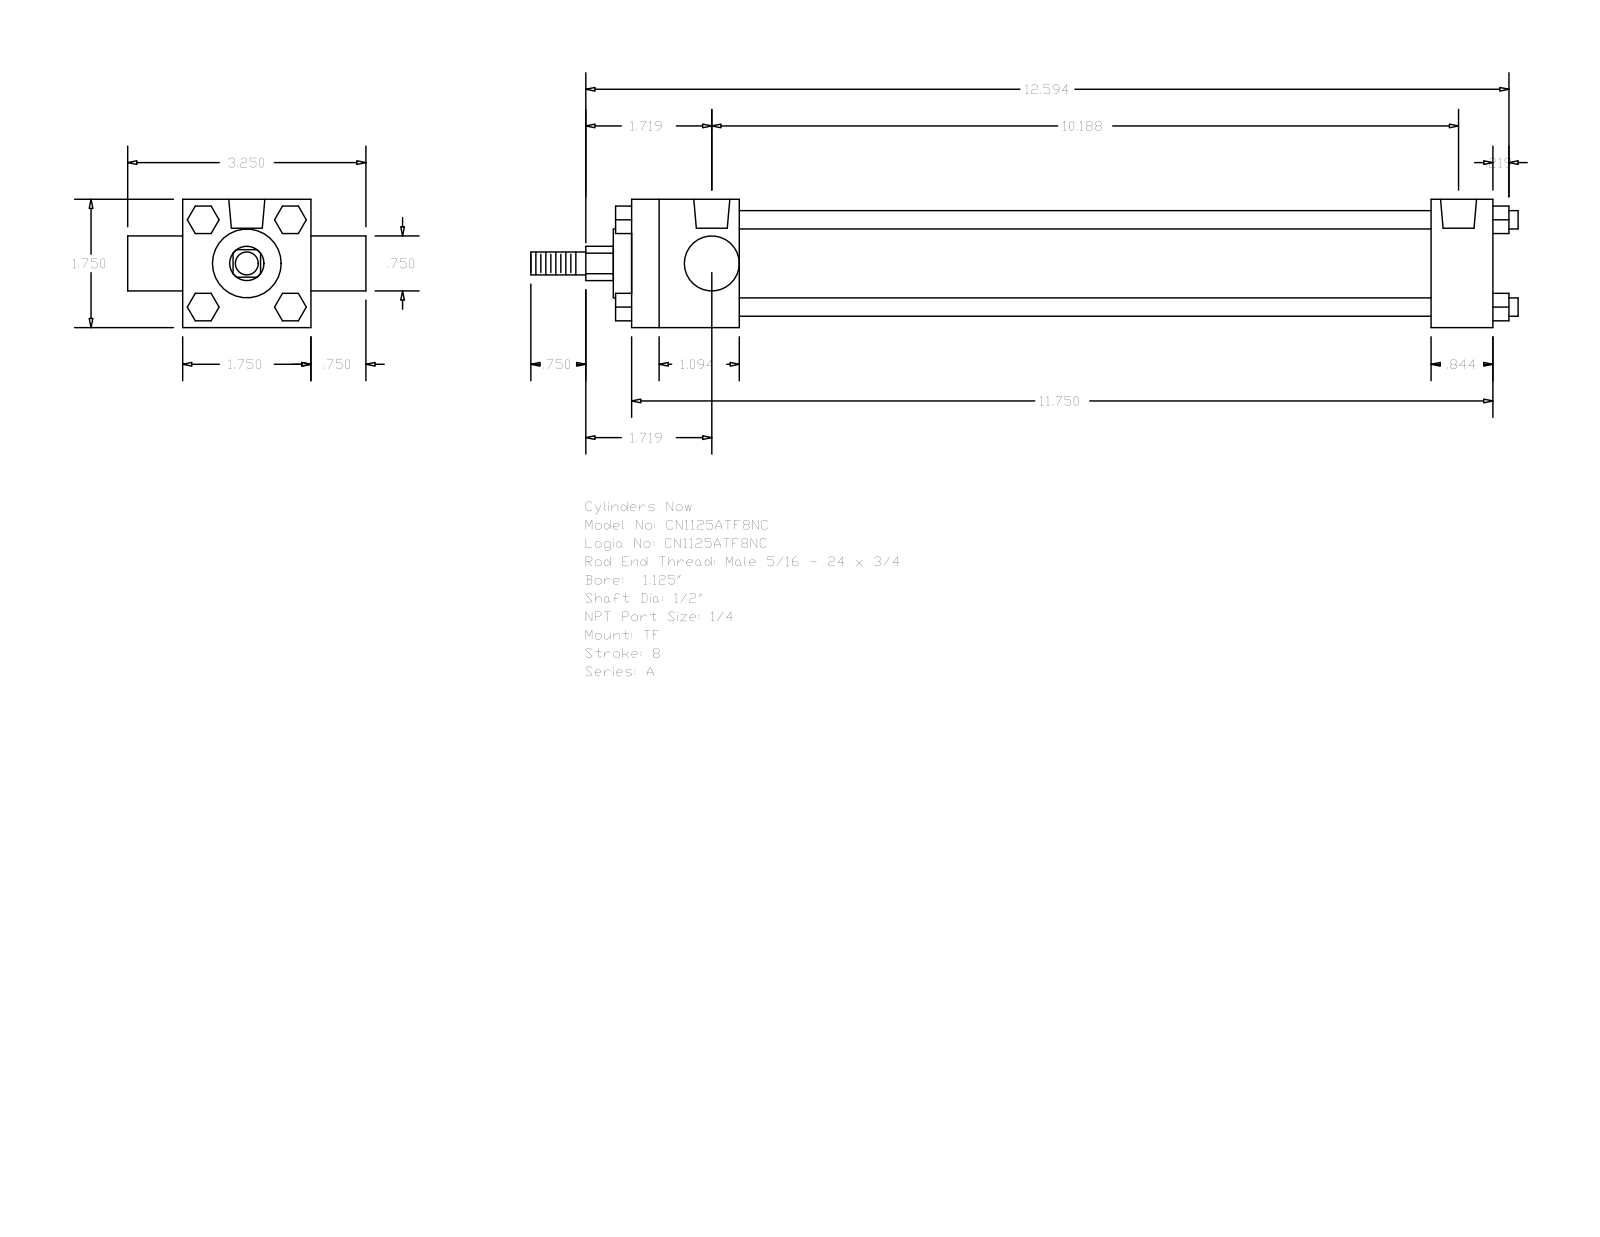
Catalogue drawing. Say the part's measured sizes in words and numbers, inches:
The part is named "A_TF__0112_0.5". Its 3-D file was written by "GSSL Pune (CONFIG_CONTROL_DESIGN)". It is 0 solids with 120 faces: 92 planar, 28 cylindrical and 0 other. Overall it measures 13.469 by 3.25 by 1.75 inches. Round holes: 3 of diameter 0.219, 2 of diameter 0.492. Round bosses or shafts: 4 of diameter 0.25, 1 of diameter 1.255, 1 of diameter 0.937, 1 of diameter 0.75, 1 of diameter 0.5, 1 of diameter 0.313. Partial cylindrical surfaces (rounded edges, fillets, slot ends): 1 of radius 0.234. The main face-to-face distances are 1.75, 11.75, 10.906, 0.844, 1.469, 9.437, 10.281, 0.75, 2.5, 0.375. The hole center spacings are 0.062, 0.063, 10.063, 10.125, 10.125, 10.187.
